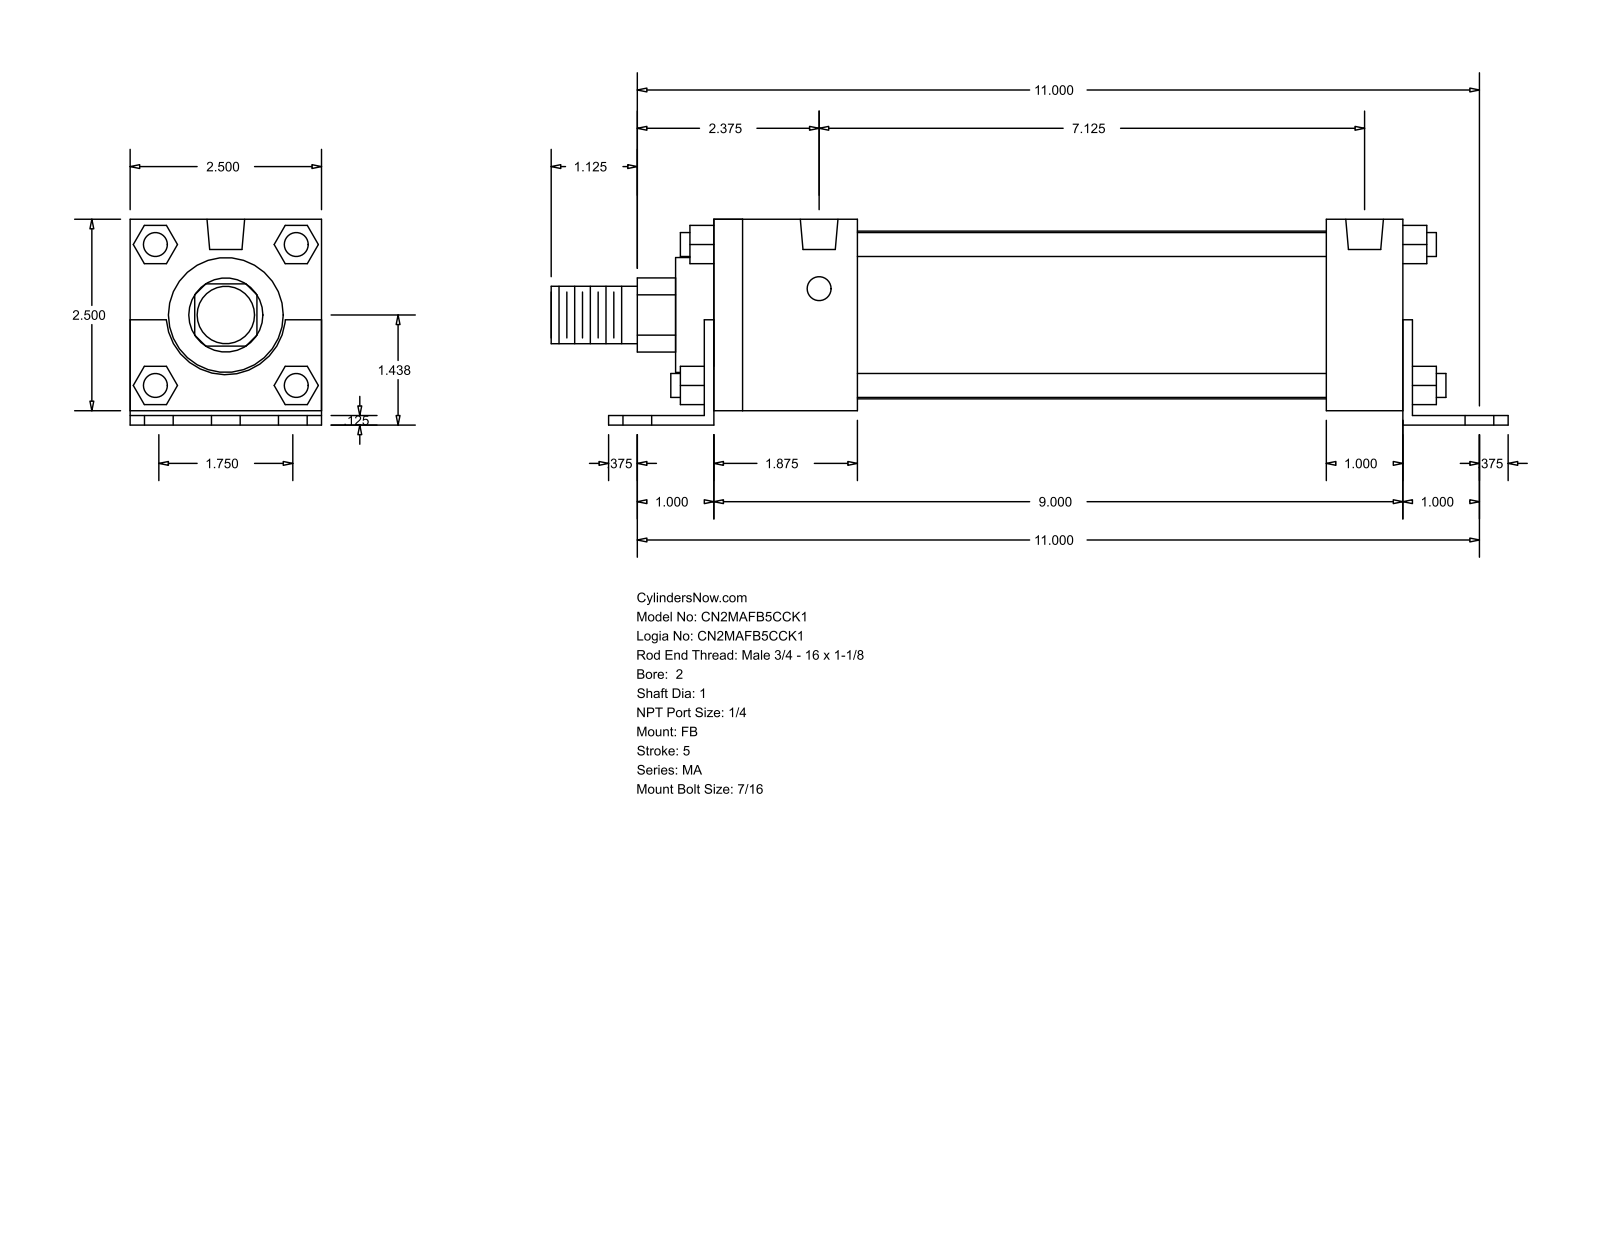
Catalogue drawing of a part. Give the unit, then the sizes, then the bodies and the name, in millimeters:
Units: millimetres
Overall size (bounding box): 317.5 × 68.26 × 63.5
Round holes (diameter × count): ⌀11.11 ×6, ⌀7.94 ×4, ⌀12.49 ×2
Round bosses / shafts (diameter × count): ⌀7.94 ×4, ⌀55.63 ×1, ⌀38.1 ×1, ⌀25.4 ×1, ⌀19.05 ×1
Partial cylindrical surfaces — rounded edges, fillets, slot ends (radius × count): R12.29 ×1, R19.81 ×1
Main face-to-face distances: 63.5, 3.17, 4.76, 68.26, 1.59, 65.09, 12.7, 3.18, 228.6, 231.78
Hole centre spacings: 22.23, 280.28, 279.4, 44.11, 44.46, 64.3, 180.97, 220.19
Bodies: 0 solids, 140 faces (105 planar, 35 cylindrical, 0 other)
Part name (STEP PRODUCT): MA_FB__0200_1
STEP written by: GSSL Pune (CONFIG_CONTROL_DESIGN)
